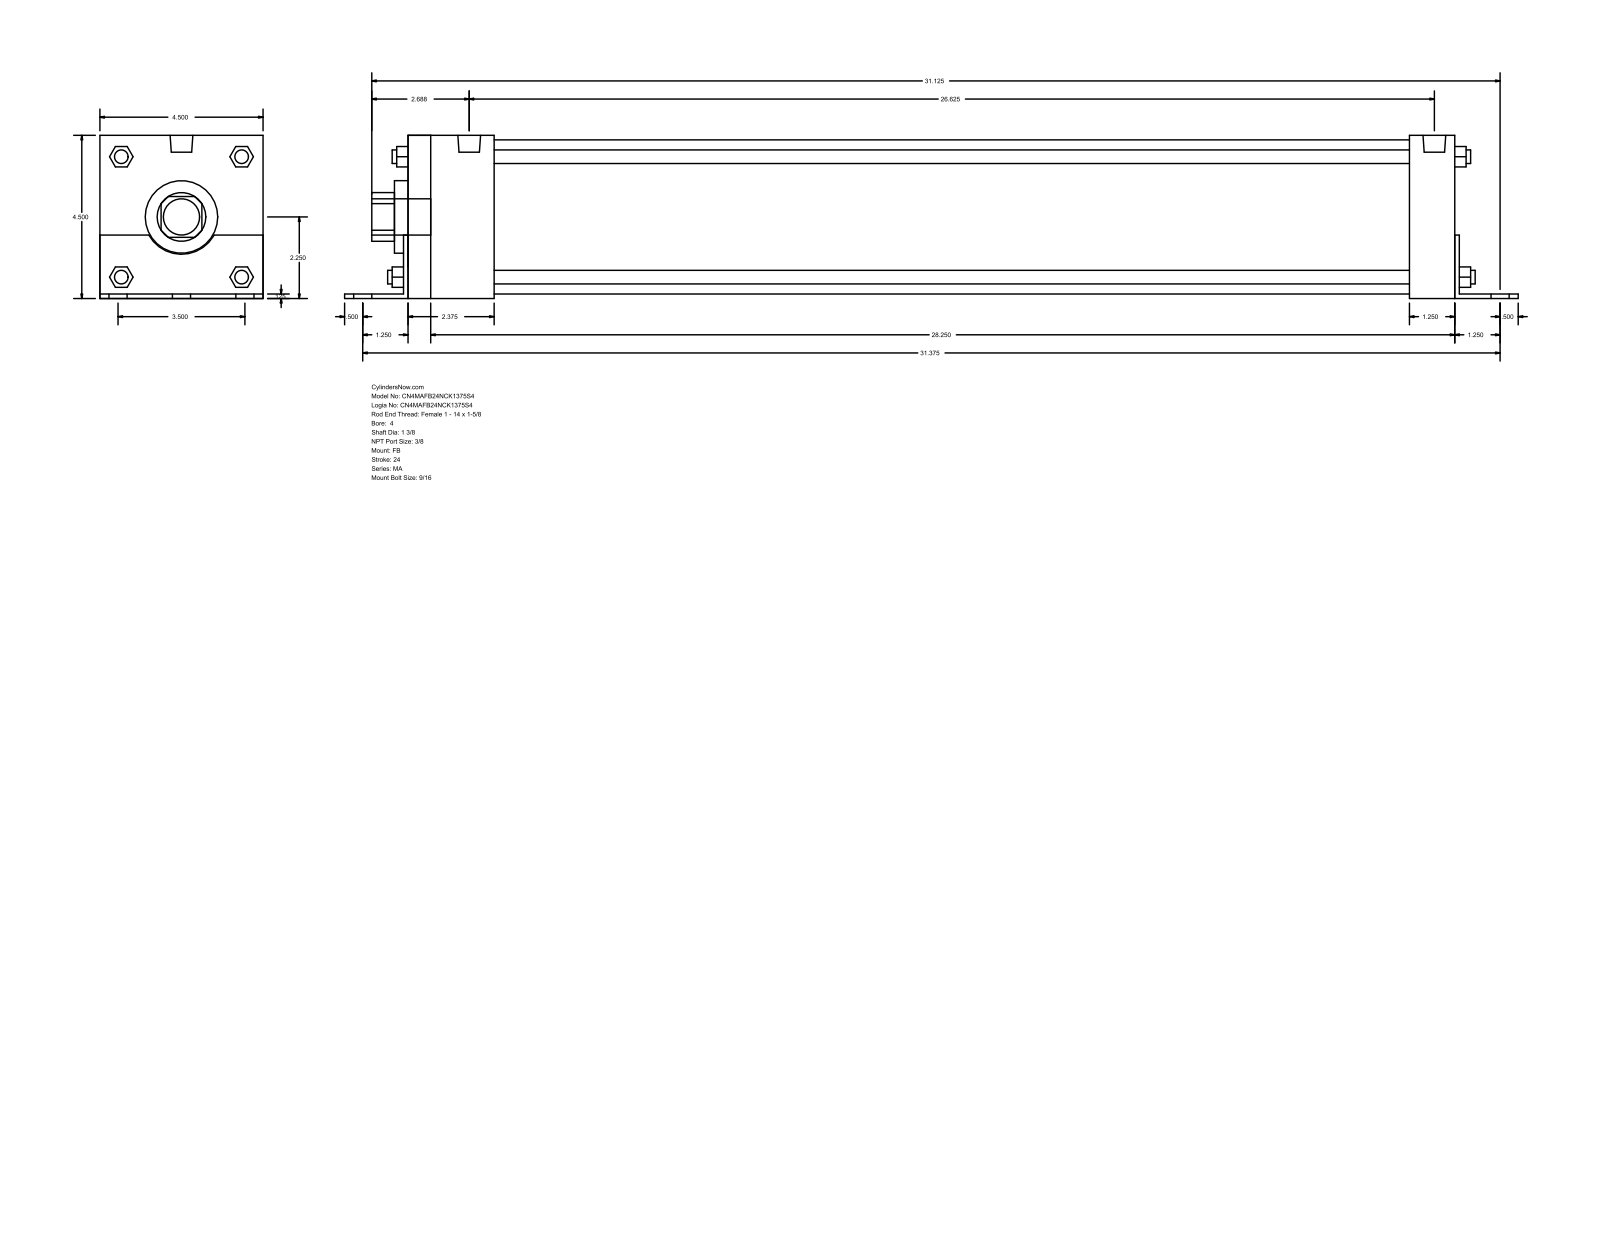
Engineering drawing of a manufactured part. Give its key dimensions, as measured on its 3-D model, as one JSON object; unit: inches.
{"part_name": "MA_FB__0400_1.375", "step_written_by": "GSSL Pune (CONFIG_CONTROL_DESIGN)", "units": "inches", "bodies": {"solids": 0, "faces": 140, "planar": 105, "cylindrical": 35, "other": 0}, "overall_size": [32.375, 4.502, 4.5], "round_holes": [[1.375, 1], [2, 1], [4.25, 1]], "round_bosses_or_shafts": [[0.563, 6], [0.437, 4], [0.375, 4], [0.627, 2], [1, 1]], "partial_cylinders_radius": [[0.672, 1], [1.03, 1]], "face_to_face_distances": [4.5, 0.125, 4.502, 0.123, 4.377, 29, 28.875, 2.375, 29.125, 1.25]}
